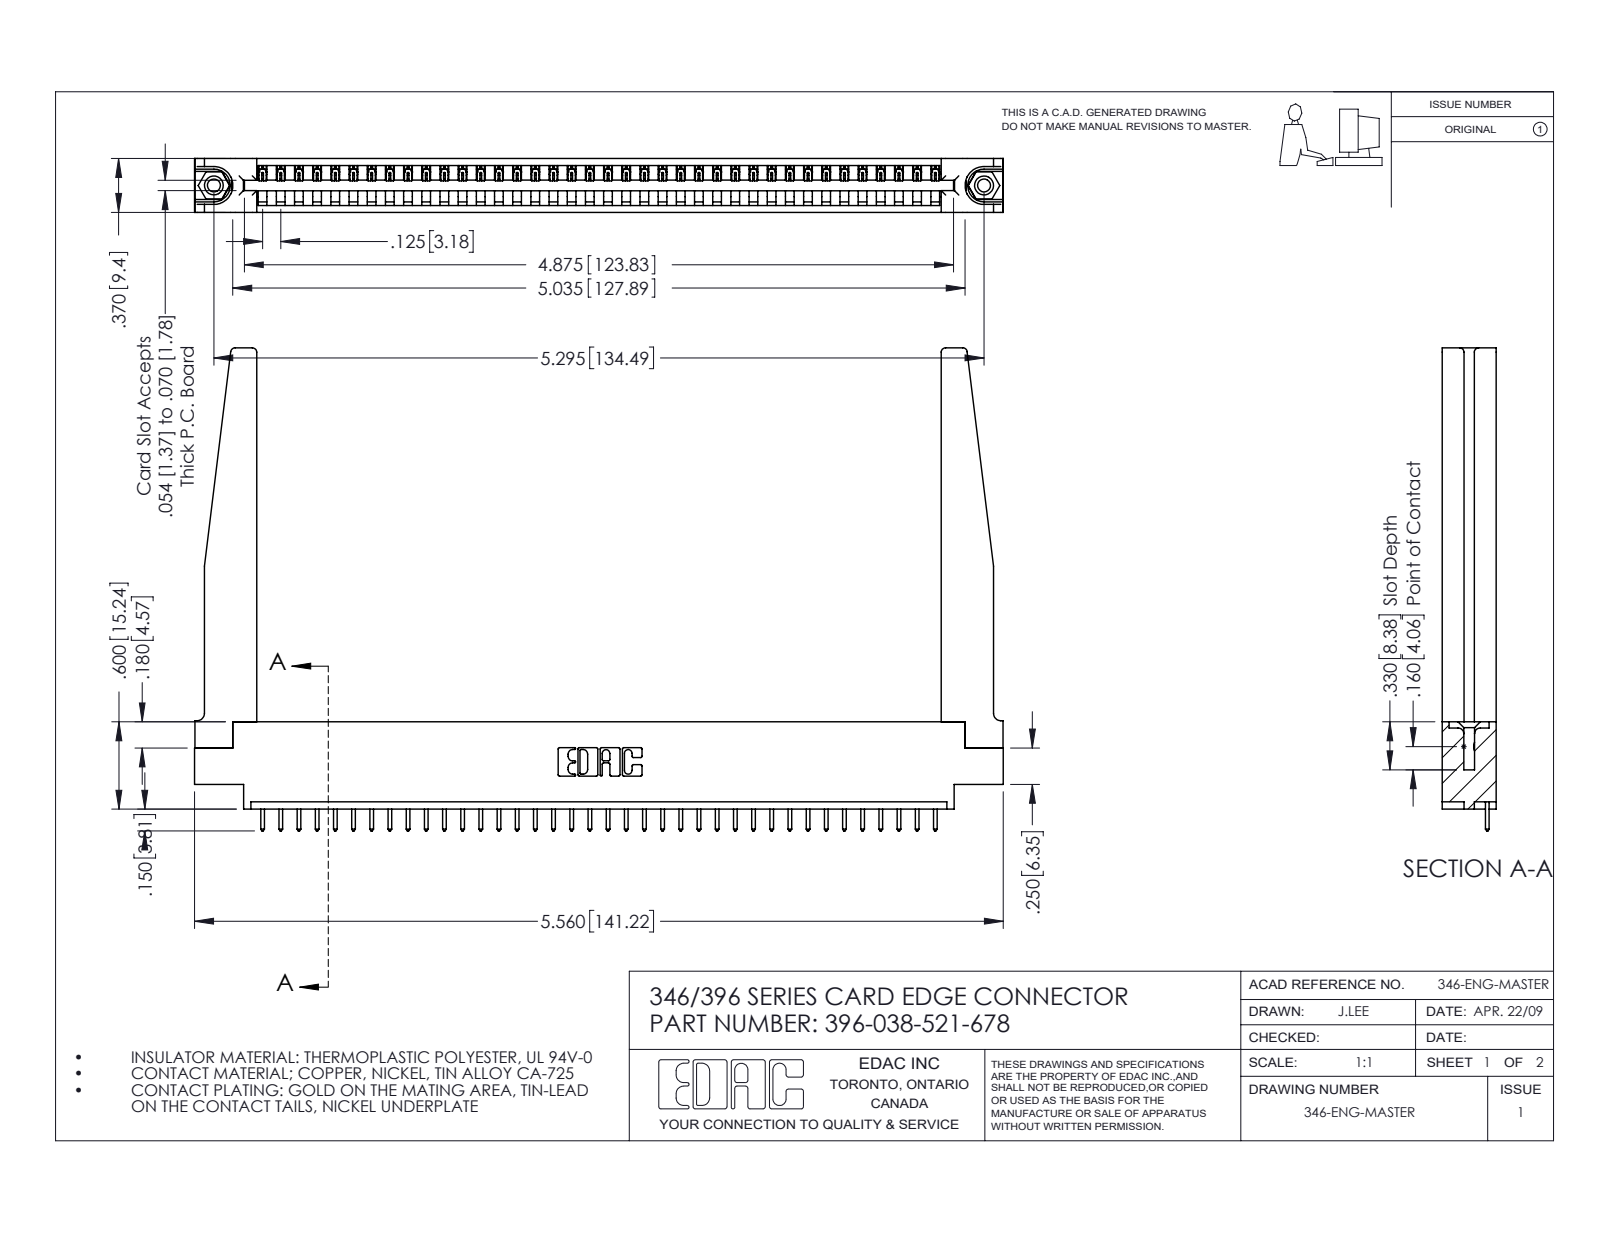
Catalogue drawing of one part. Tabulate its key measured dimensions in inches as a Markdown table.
| quantity | value |
| --- | --- |
| part name | 345-292-001_345-293-121; 396-038-521-678; 346 Part_0.170 Offset - 0.156 Dia-TH; 345-250-001_345-250-001-102 (+1 more) |
| STEP written by | SolidWorks 2016 (CONFIG_CONTROL_DESIGN) |
| units | inches |
| bodies | 43 solids, 2564 faces (1742 planar, 770 cylindrical, 52 other) |
| overall size | 5.56 × 3.32 × 0.37 |
| volume | 1.229 in³ |
| surface area | 35.28 in² |
| round holes (diameter × count) | 0.089 × 2, 0.125 × 2, 0.156 × 2, 0.064 × 1 |
| round bosses / shafts (diameter × count) | 0.155 × 2 |
| partial cylindrical surfaces (radius × count) | 0.006 × 76, 0.01 × 76, 0.01 × 22, 0.03 × 8, 0.007 × 6, 0.031 × 6, 0.026 × 3, 0.031 × 2 |
| main face-to-face distances | 0.37, 0.048, 0.322, 0.072, 0.148, 0.15, 0.25, 0.298, 0.025, 0.222 |
| hole center spacings | 0.246, 5.086, 5.295 |
